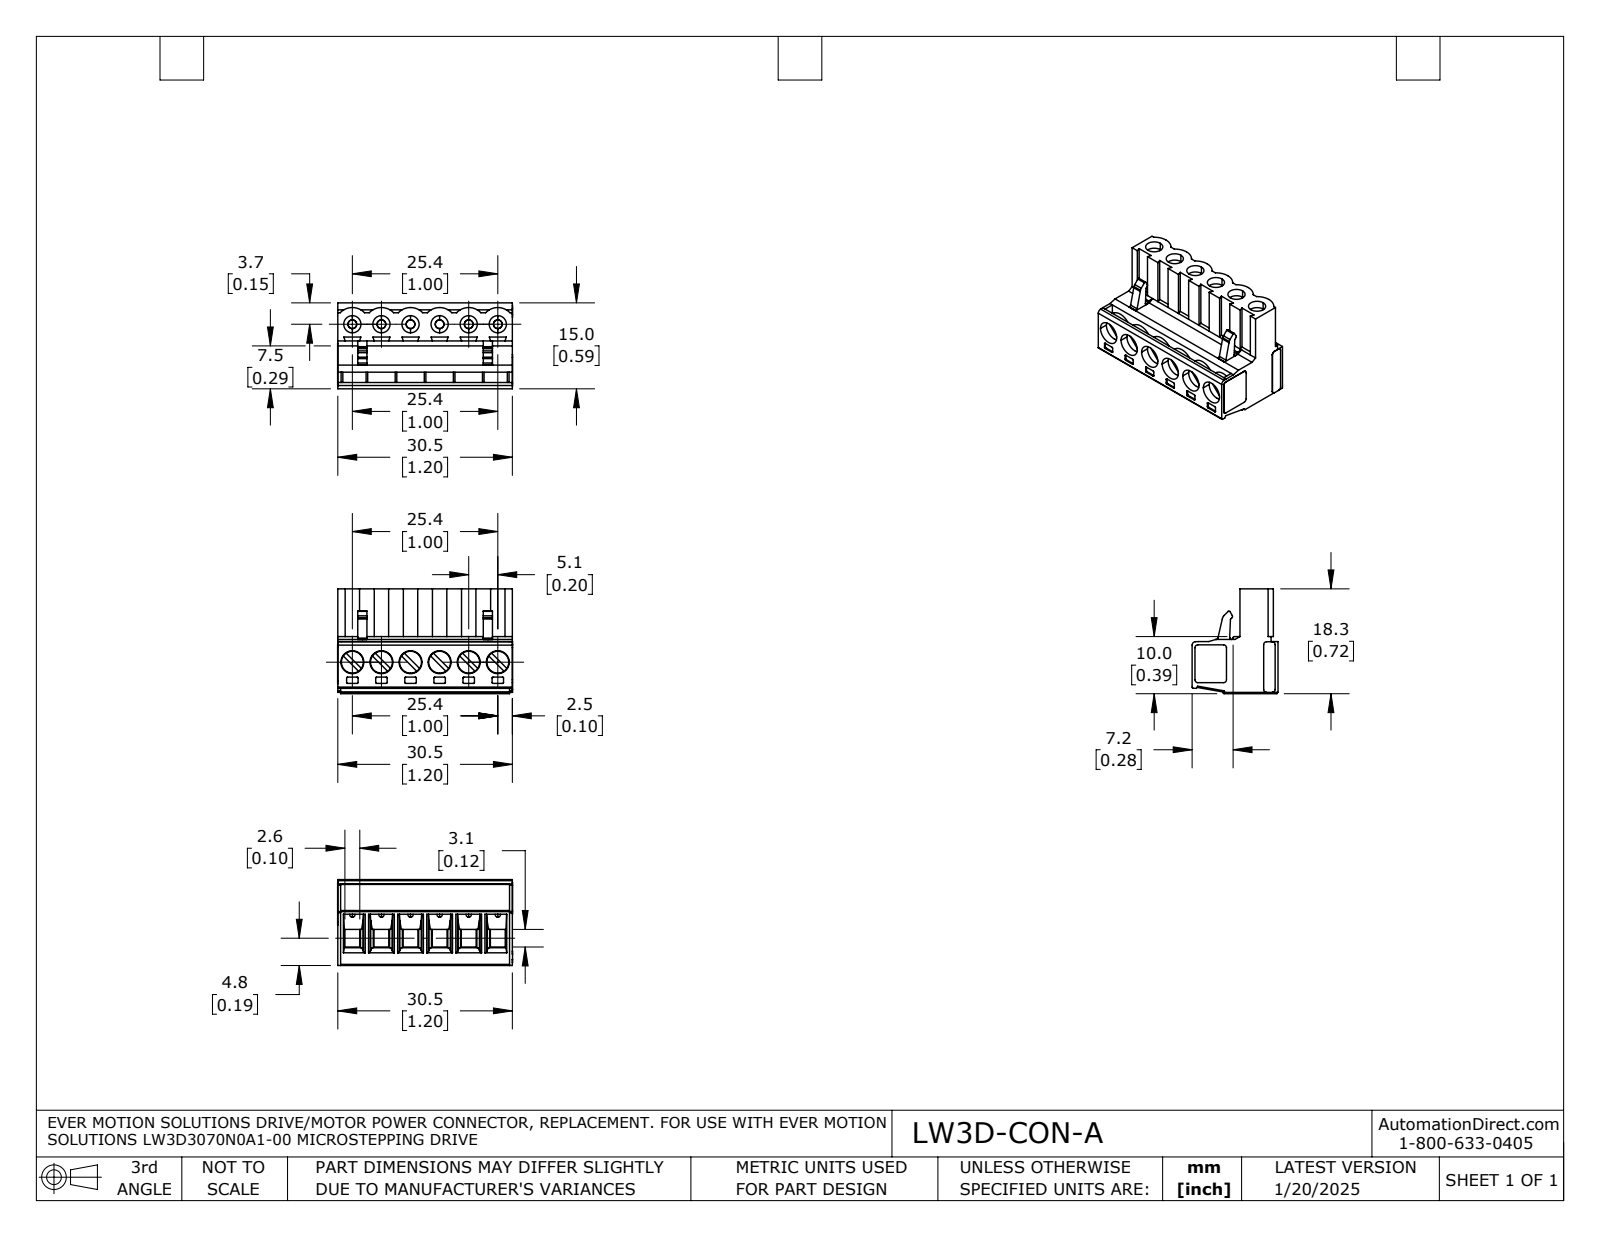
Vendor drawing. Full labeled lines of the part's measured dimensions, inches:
Part name (STEP PRODUCT): LW3D-CON-A
STEP written by: SolidWorks 2021 (AUTOMOTIVE_DESIGN)
Units: inches
Bodies: 19 solids, 1210 faces (970 planar, 213 cylindrical, 27 other)
Overall size (bounding box): 1.202 × 0.72 × 0.591
Volume: 0.262 in³ · Surface area: 10.26 in²
Round holes (diameter × count): ⌀0.118 ×12, ⌀0.059 ×6, ⌀0.06 ×6, ⌀0.157 ×6
Round bosses / shafts (diameter × count): ⌀0.15 ×6, ⌀0.015 ×1
Partial cylindrical surfaces — rounded edges, fillets, slot ends (radius × count): R0.006 ×24, R0.012 ×13, R0.02 ×12, R0.005 ×10, R0.102 ×6, R0.115 ×6, R0.008 ×5, R0.007 ×4
Main face-to-face distances: 0.2, 0.4, 0.6, 0.161, 0.197, 0.039, 0.361, 0.8, 0.356, 0.561
Hole centre spacings: 0.2, 0.4, 0.6, 0.8, 1
